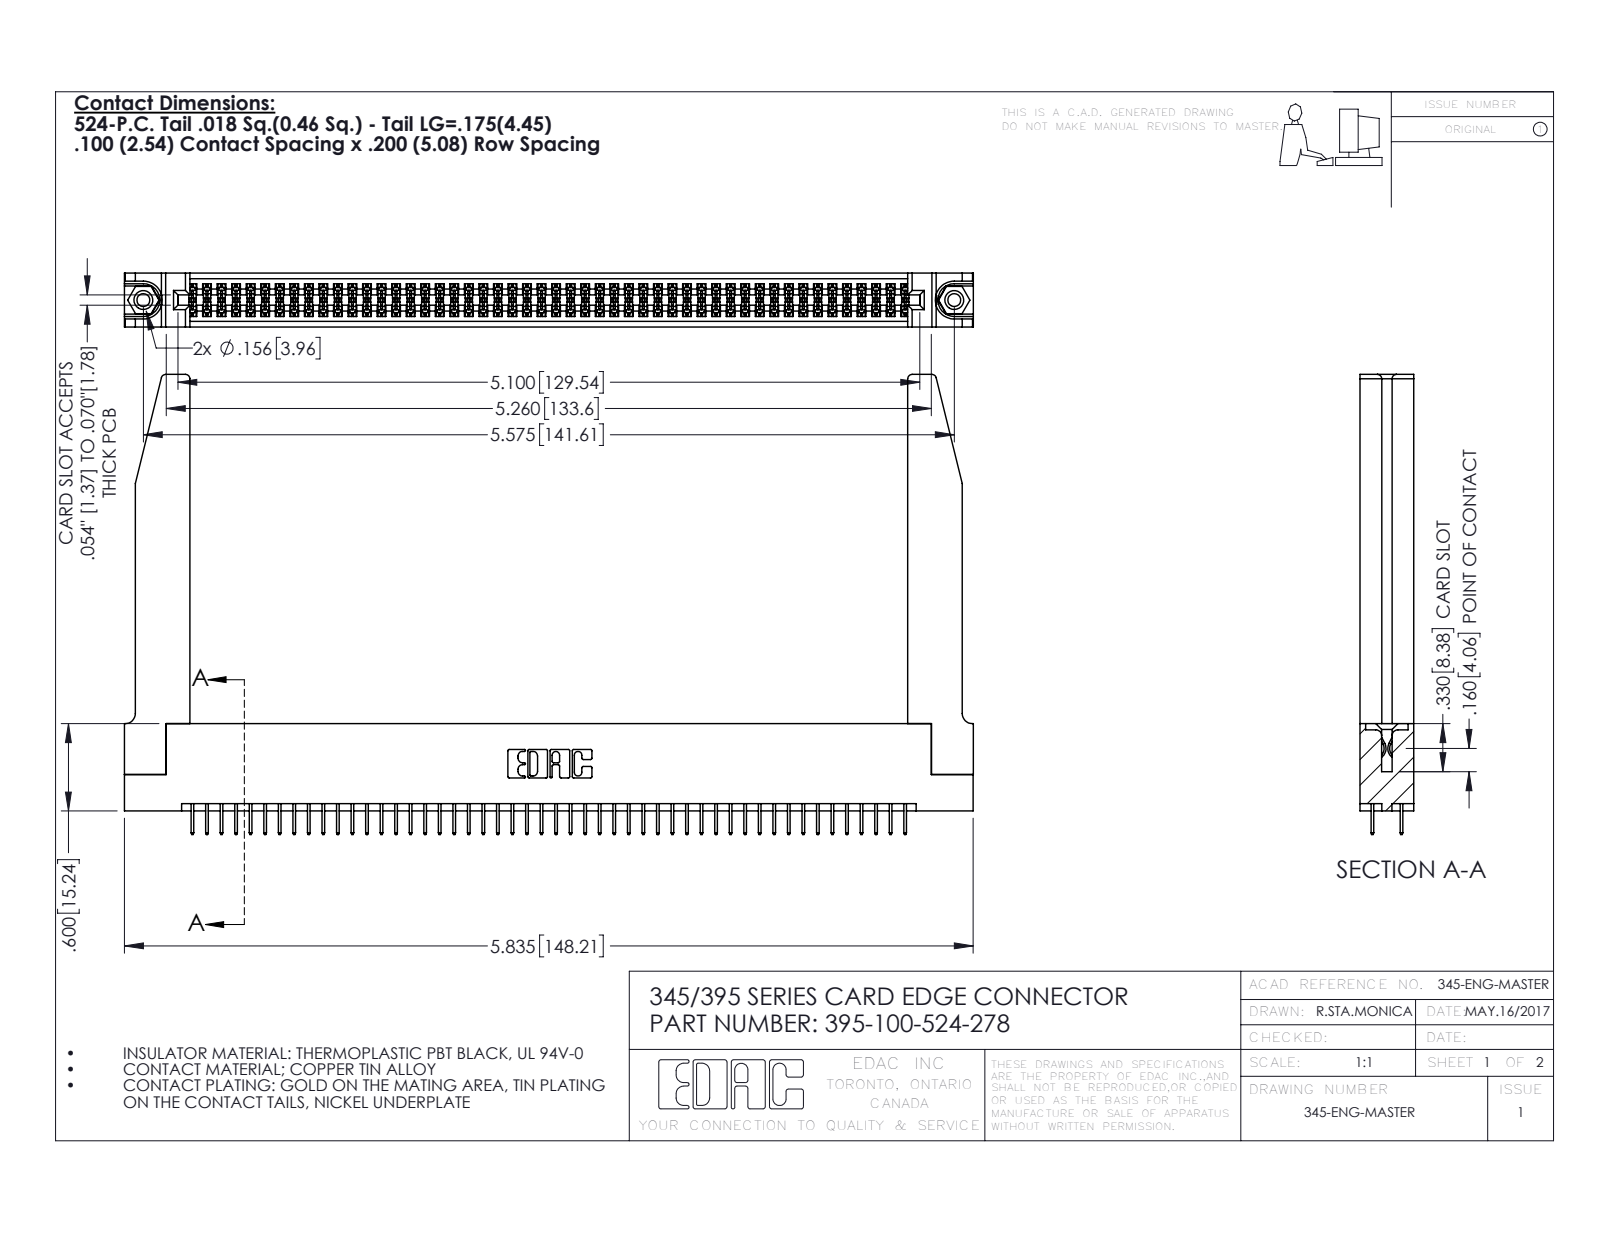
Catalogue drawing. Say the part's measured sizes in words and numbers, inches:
The part is named "395-100-524-278; 345-220-078_345-220-078; 345-292-001_345-293-124; 345 Part_Flush Mounting Lugs - 0.156 Dia-TH (+1 more)". Its 3-D file was written by "SolidWorks 2016 (CONFIG_CONTROL_DESIGN)". It is 105 solids with 5760 faces: 4122 planar, 1586 cylindrical and 52 other. Overall it measures 5.836 by 3.162 by 0.37 inches. Its volume is 1.348 cubic inches and its surface area 43.04 square inches. Round holes: 2 of diameter 0.089, 2 of diameter 0.125, 2 of diameter 0.156, 1 of diameter 0.064. Round bosses or shafts: 2 of diameter 0.155. Partial cylindrical surfaces (rounded edges, fillets, slot ends): 150 of radius 0.006, 22 of radius 0.01, 8 of radius 0.03, 6 of radius 0.007, 6 of radius 0.031, 3 of radius 0.026, 2 of radius 0.014, 2 of radius 0.019. The main face-to-face distances are 0.37, 0.072, 0.298, 0.2, 0.098, 0.272, 0.025, 0.225, 0.072, 0.15. The hole center spacings are 0.27, 5.339, 5.575.
